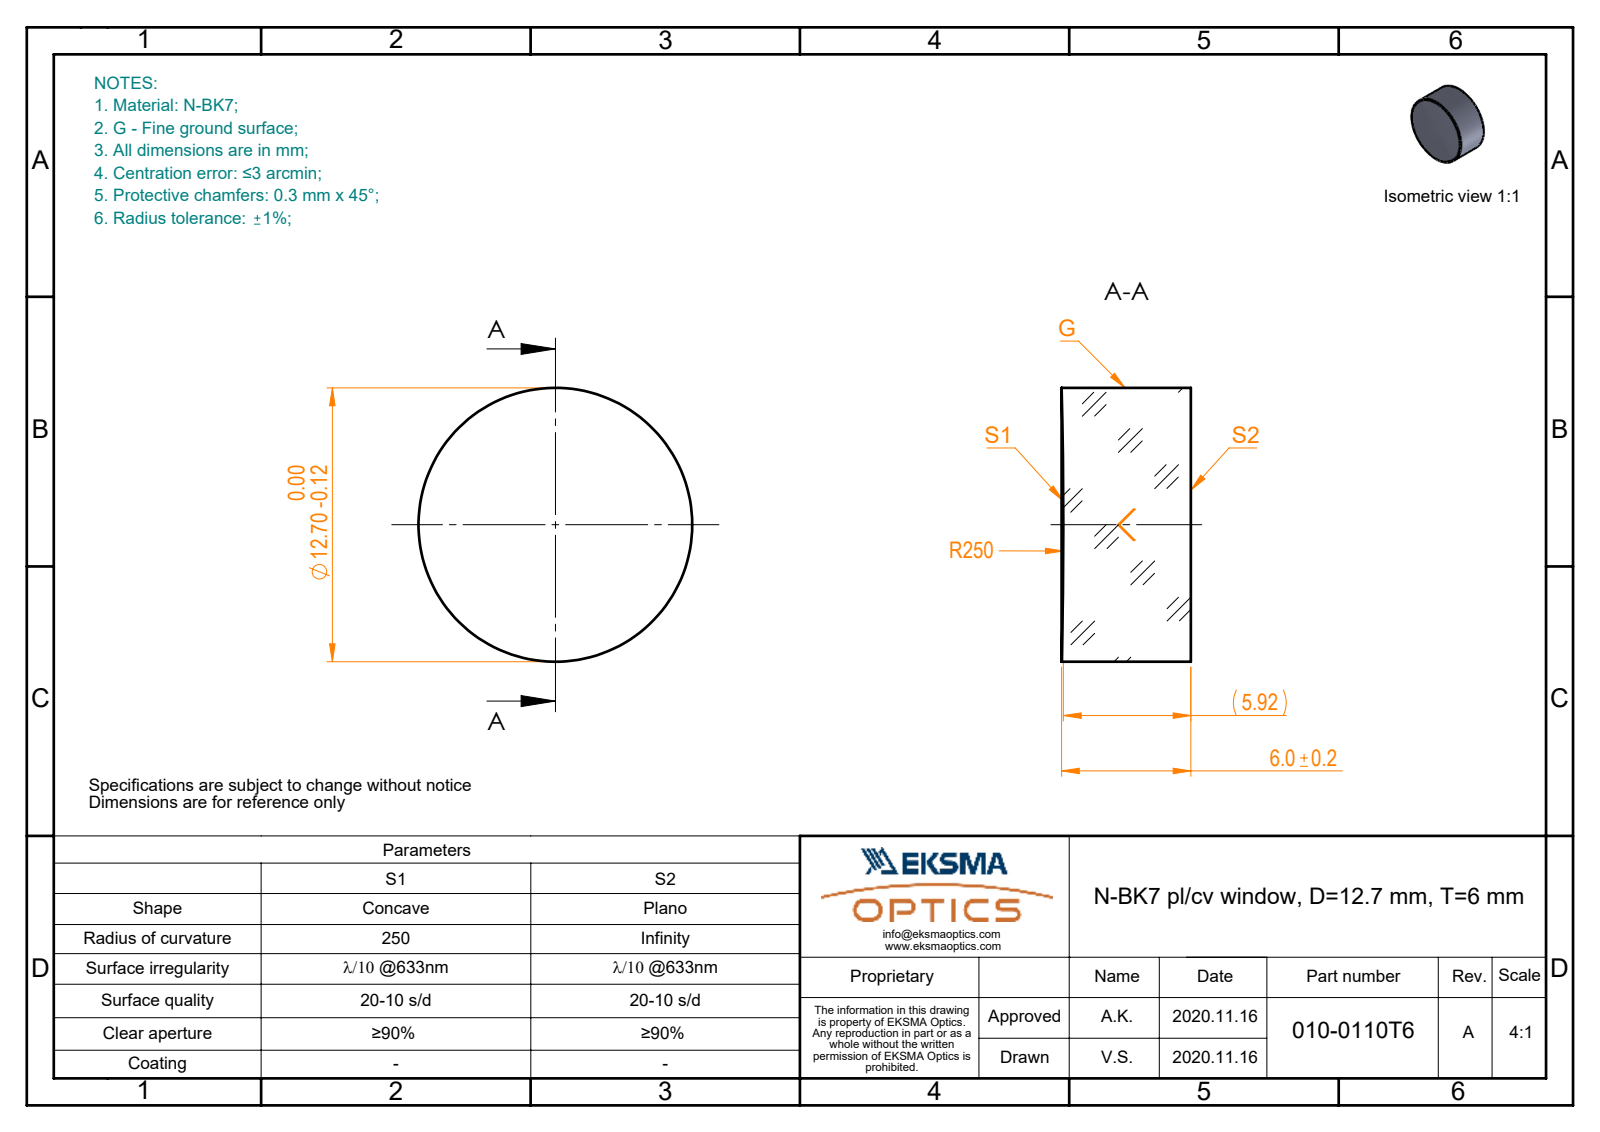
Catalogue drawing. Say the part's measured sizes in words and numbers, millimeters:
The part is named "010-0110T6_N-BK7_PCV_window". Its 3-D file was written by "SolidWorks 2019 (CONFIG_CONTROL_DESIGN)". It is 1 solid with 5 faces: 1 planar, 2 cylindrical and 2 other. Overall it measures 12.7 by 12.7 by 6 millimeters. Its volume is 755 cubic millimeters and its surface area 493 square millimeters. Round bosses or shafts: 1 of diameter 12.7.
